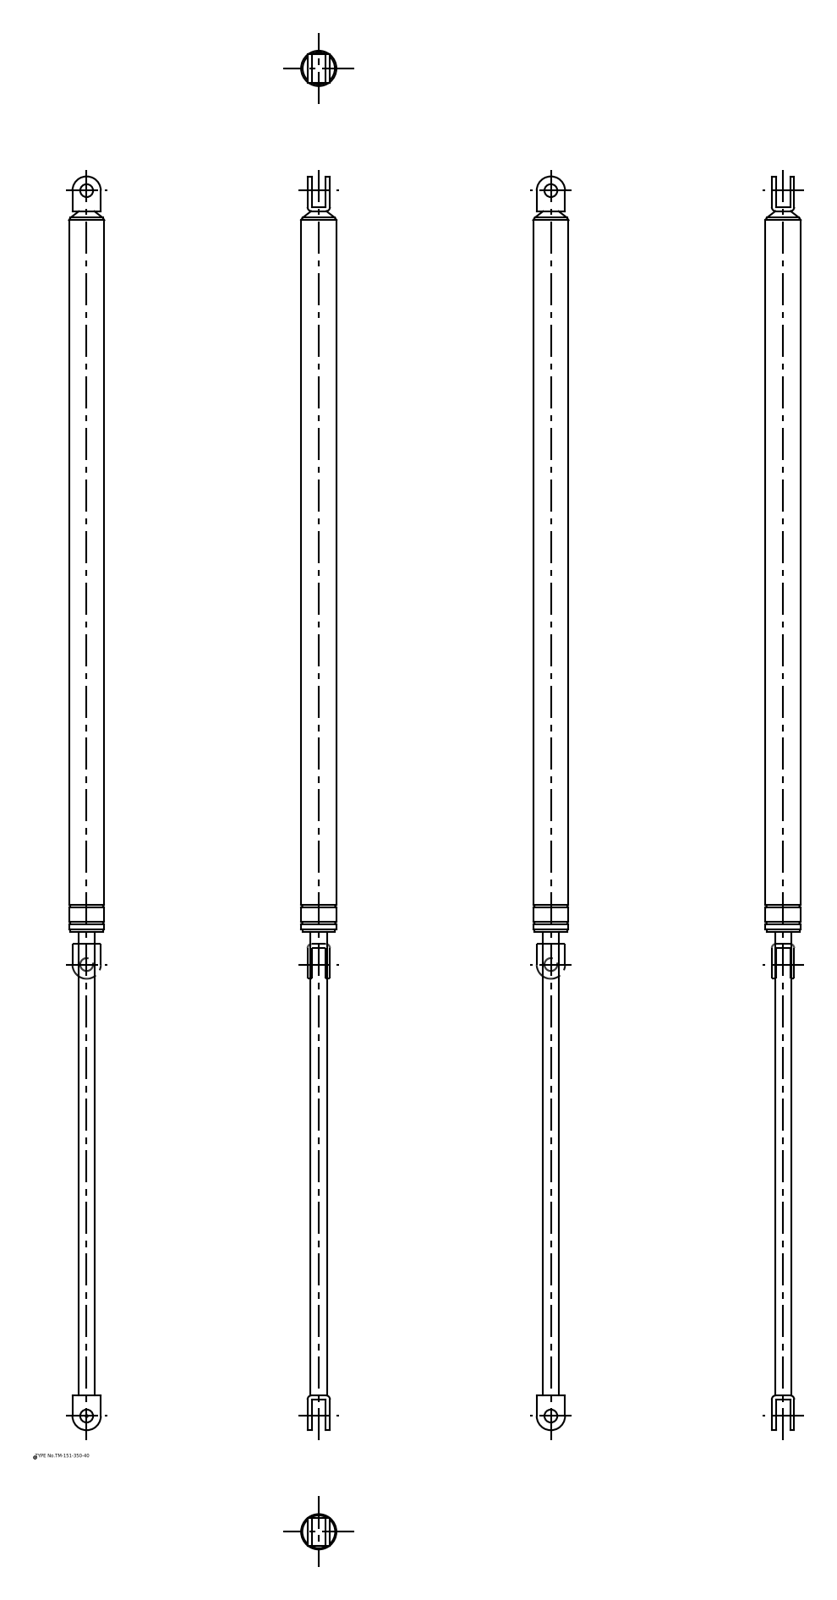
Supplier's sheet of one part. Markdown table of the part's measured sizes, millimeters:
| quantity | value |
| --- | --- |
| part name | TM_151_350_40; TM_151_350_40_div |
| STEP written by | spGate 16.7.1 (AUTOMOTIVE_DESIGN) |
| units | millimeters |
| bodies | 2 solids, 64 faces (22 planar, 32 cylindrical, 10 other) |
| overall size | 972 × 28.2 × 28.2 |
| volume | 379 410 mm³ |
| surface area | 68 998 mm² |
| round holes (diameter × count) | 10 × 2 |
| round bosses / shafts (diameter × count) | 28.2 × 1, 27.4 × 1, 25.5 × 1, 12.5 × 1 |
| partial cylindrical surfaces (radius × count) | 3.2 × 4, 11 × 2 |
| main face-to-face distances | 3.2, 14.2, 17.4, 11, 22, 921.2, 362.2, 924.4, 562.2, 559 |
| hole center spacings | 950 |
